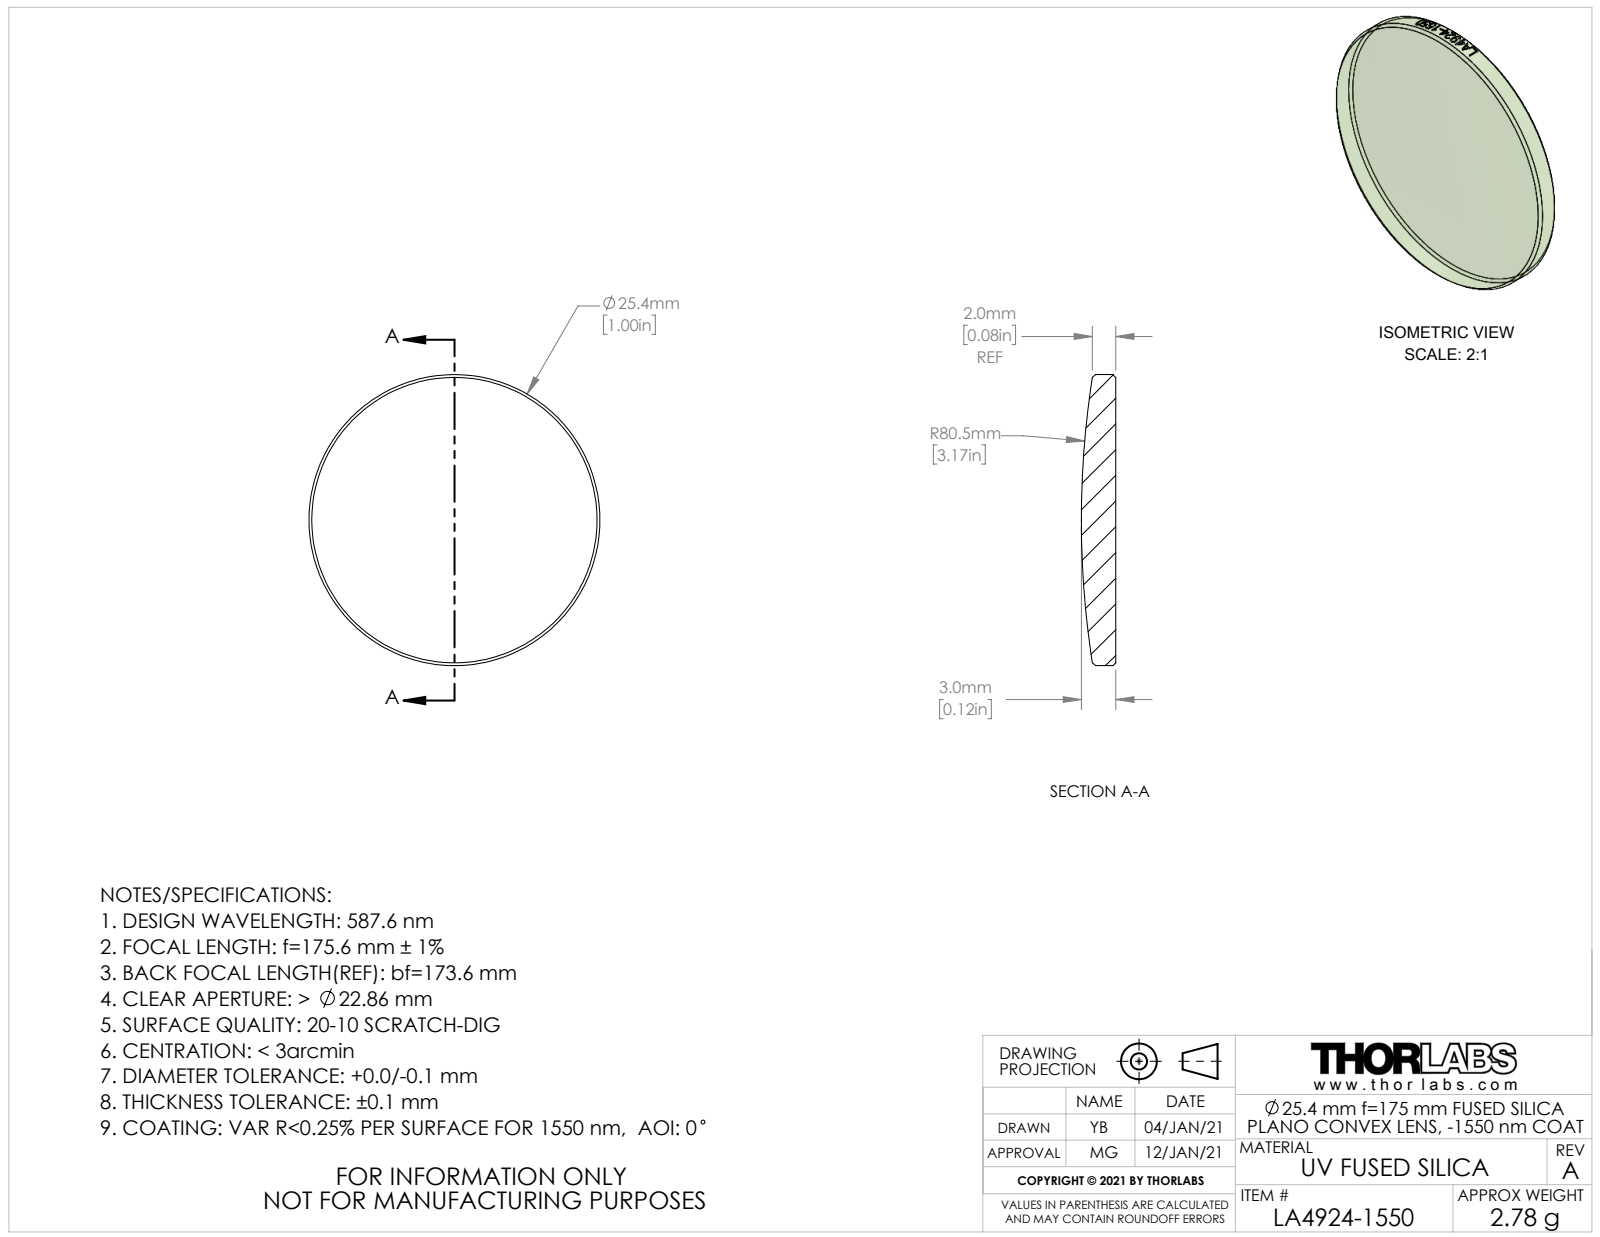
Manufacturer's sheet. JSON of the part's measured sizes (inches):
{"part_name": "CTN015941-E0W", "step_written_by": "SolidWorks 2018 (AUTOMOTIVE_DESIGN)", "units": "inches", "bodies": {"solids": 1, "faces": 27, "planar": 1, "cylindrical": 20, "other": 6}, "overall_size": [1, 1, 0.118], "volume_in3": 0.077, "surface_area_in2": 1.79, "round_bosses_or_shafts": [[1, 1]]}
